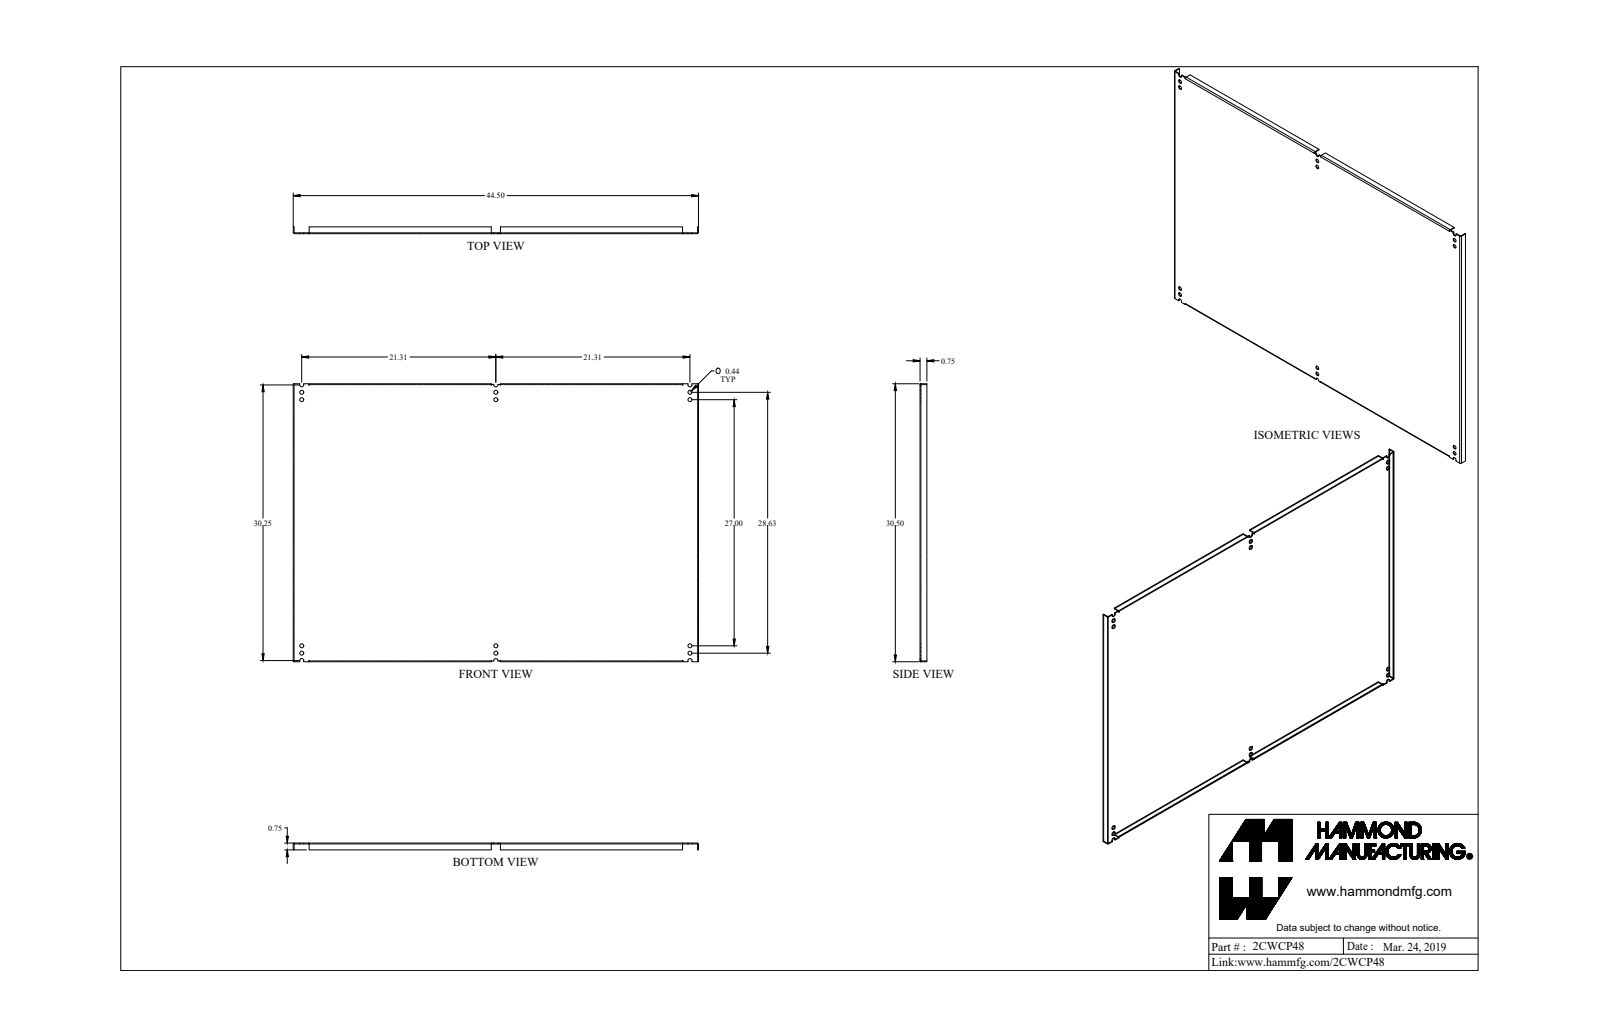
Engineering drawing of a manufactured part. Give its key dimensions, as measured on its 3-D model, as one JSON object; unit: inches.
{"part_name": "2CWCP48", "step_written_by": "SolidWorks 2018 (AUTOMOTIVE_DESIGN)", "units": "inches", "bodies": {"solids": 3, "faces": 111, "planar": 78, "cylindrical": 33, "other": 0}, "overall_size": [44.5, 30.497, 1.07], "volume_in3": 137, "surface_area_in2": 2902, "round_holes": [[0.437, 12], [0.307, 1], [0.445, 1]], "round_bosses_or_shafts": [[1, 1]], "partial_cylinders_radius": [[0.048, 4], [0.143, 4], [0.219, 4], [0.219, 2]], "face_to_face_distances": [0.095, 30.402, 44.405, 30.497, 30.307, 44.5, 44.31, 0.75, 0.655, 0.096], "hole_center_spacings": [21.313, 21.328, 34.398, 35.039, 35.04, 35.688, 42.626, 42.634]}
